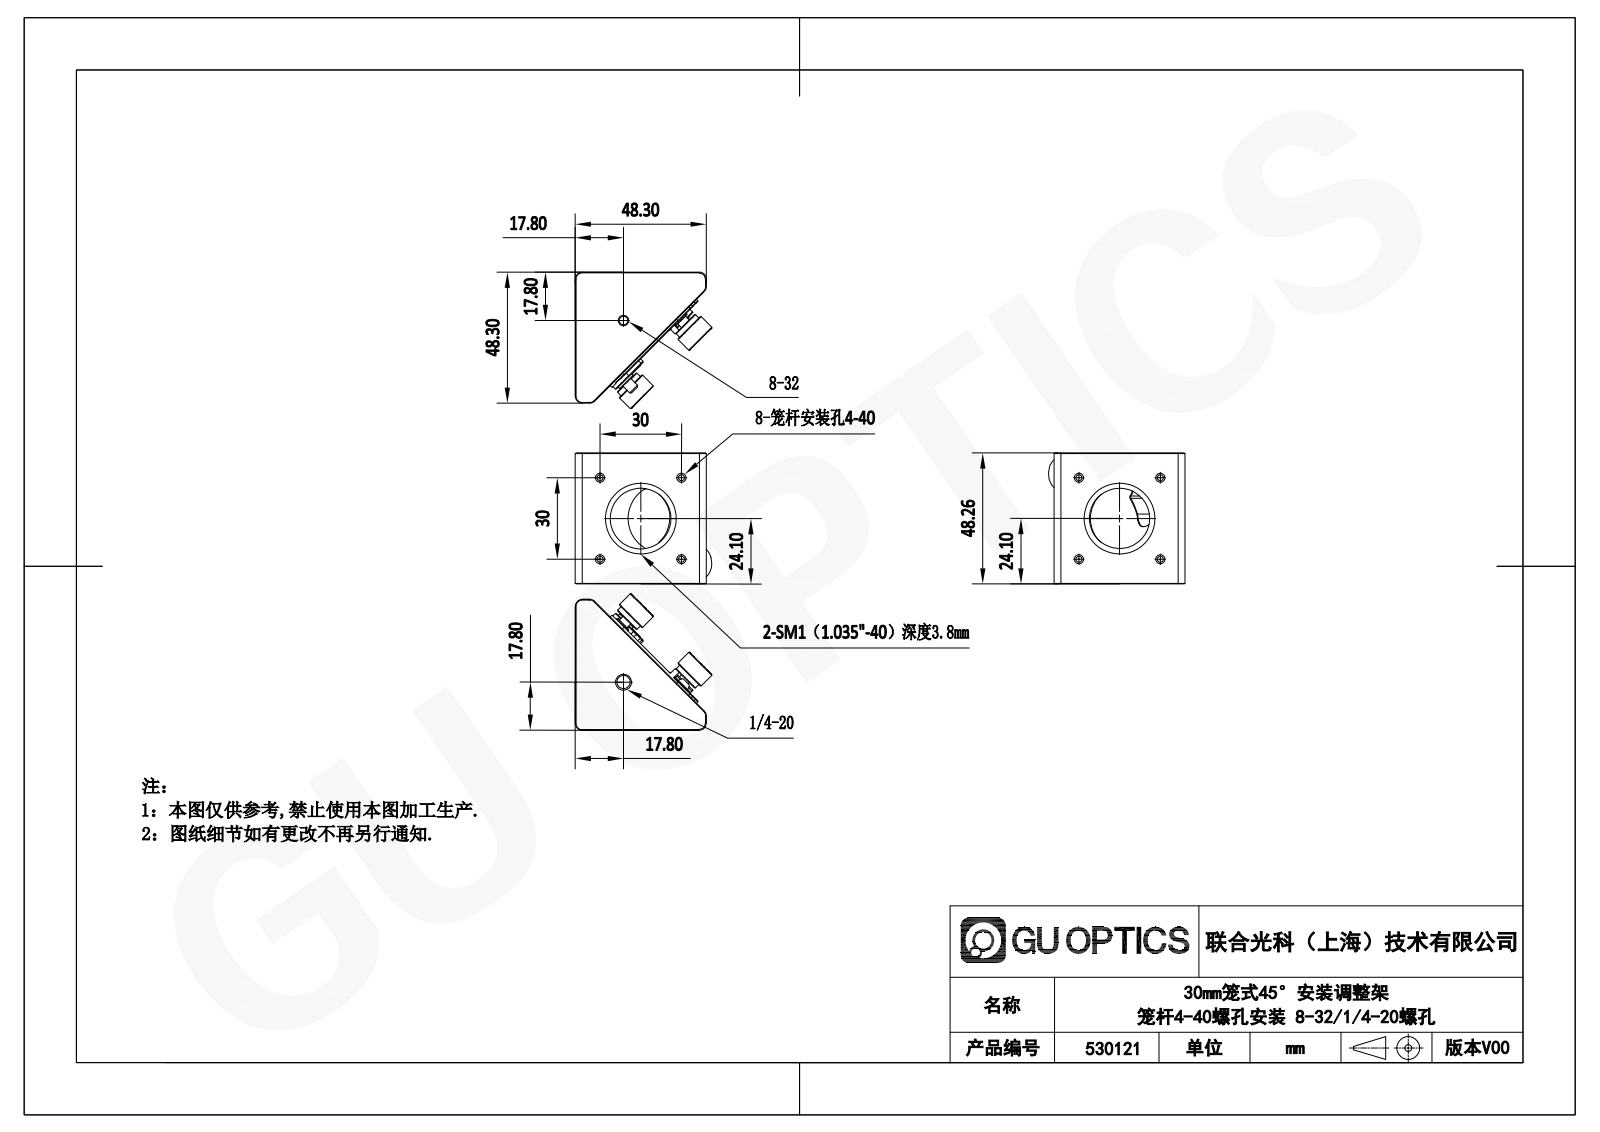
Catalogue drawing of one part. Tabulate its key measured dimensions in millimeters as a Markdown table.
| quantity | value |
| --- | --- |
| part name | 530121 |
| STEP written by | SolidWorks 2020 (CONFIG_CONTROL_DESIGN) |
| units | millimeters |
| bodies | 32 solids, 588 faces (272 planar, 173 cylindrical, 143 other) |
| overall size | 54.02 × 54.02 × 48.26 |
| volume | 49 020 mm³ |
| surface area | 26 555 mm² |
| round holes (diameter × count) | 2.26 × 8, 2.9 × 3, 2.99 × 3, 3.5 × 3, 3.56 × 3, 3.7 × 3, 3.75 × 3, 7 × 3, 1.6 × 2, 2.4 × 2, 2.8 × 2, 4 × 2 |
| round bosses / shafts (diameter × count) | 1.5 × 5, 12 × 3, 10 × 3, 4 × 3, 2 × 3, 6.8 × 2, 6 × 2, 5.5 × 2 |
| partial cylindrical surfaces (radius × count) | 0.79 × 30, 1 × 7, 0.93 × 6, 2.54 × 5, 0.79 × 4, 1.27 × 4, 4.32 × 4, 6.35 × 4 |
| main face-to-face distances | 1.14, 48.26, 4.14, 3, 10.11, 7.11, 5.97, 8.38, 5.38, 4.24 |
| hole center spacings | 22.81, 30, 33.02, 34.38, 36.9, 45.63, 5.46, 25.18 |
